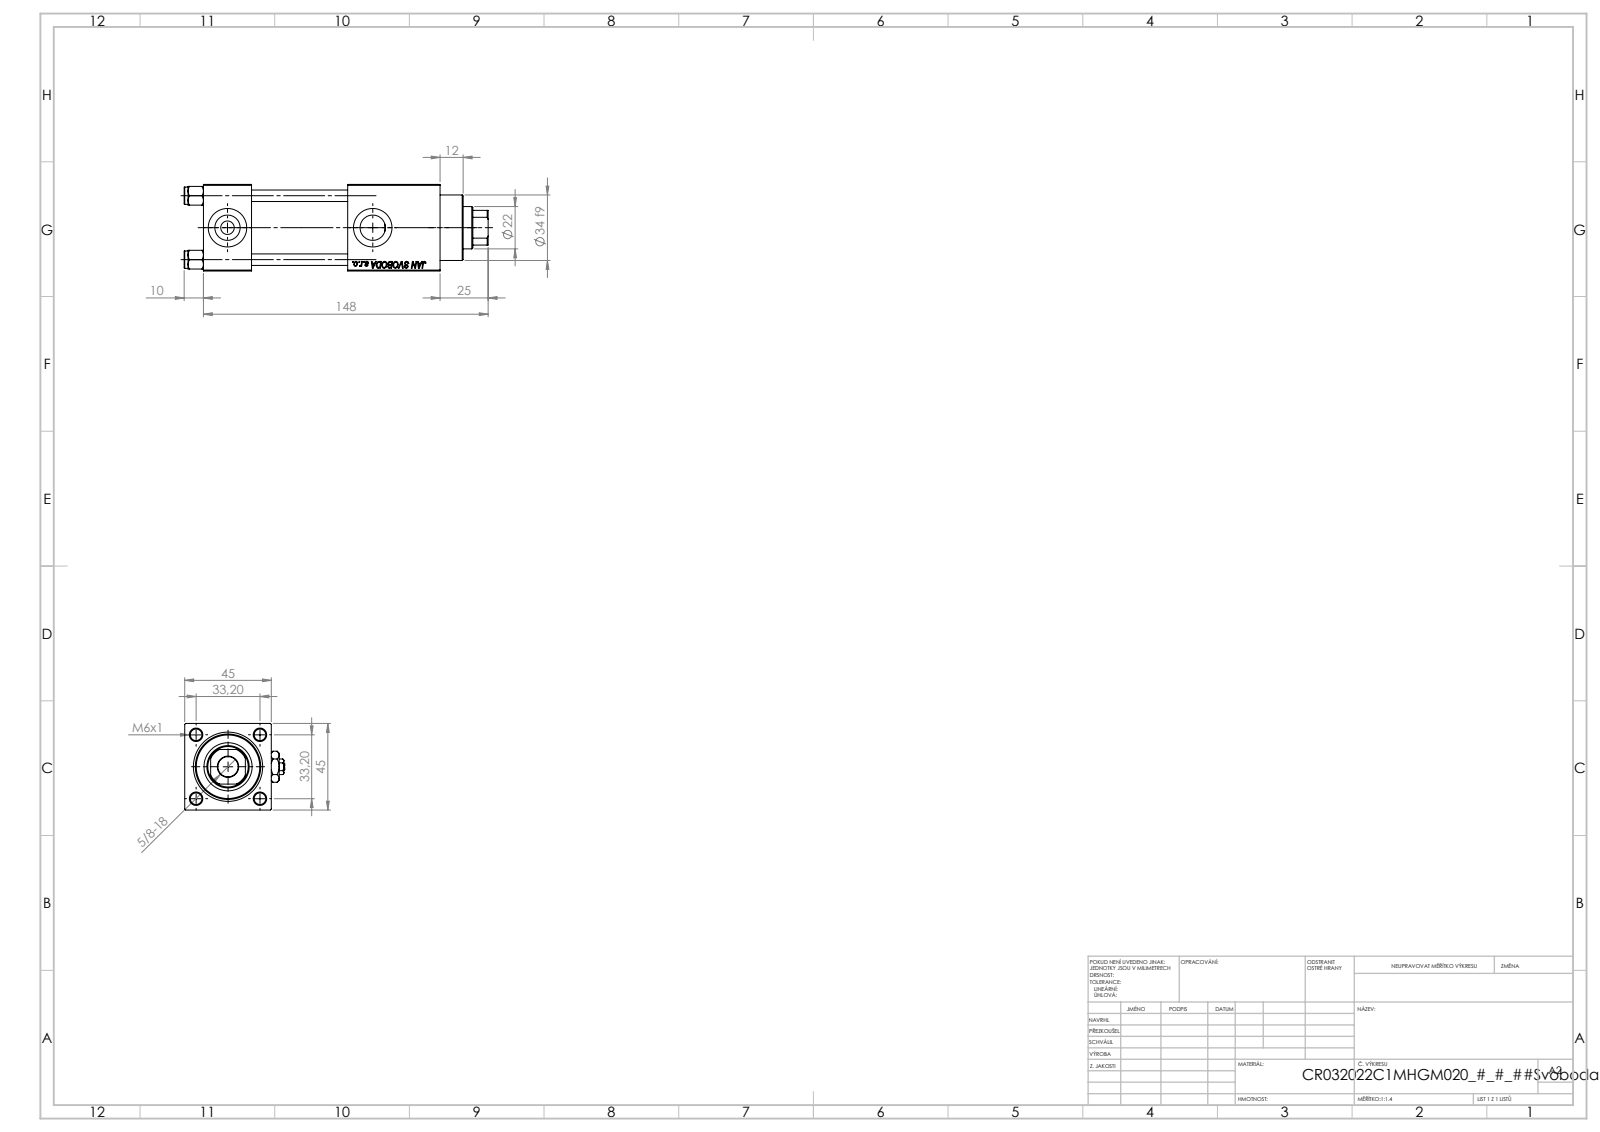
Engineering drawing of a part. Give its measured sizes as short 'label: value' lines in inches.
name: V215CR_VCP_C; V215_VC_A; V215CR_C_Body; NUT_M5_C (+2 more)
written by: SolidWorks 2019 (CONFIG_CONTROL_DESIGN)
unit: in
bodies: 12 solids, 1195 faces (549 planar, 90 cylindrical, 556 other)
size: 6.22 × 2.047 × 1.772
volume: 12.76 in³; area: 111.7 in²
holes: 4× ⌀0.236, 2× ⌀0.276, 2× ⌀0.518, 2× ⌀0.787, 1× ⌀0.413, 1× ⌀0.866, 1× ⌀0.945, 1× ⌀0.984, 1× ⌀1.26, 1× ⌀1.299
bosses: 4× ⌀0.354, 1× ⌀1.496, 1× ⌀1.339
rounds: 1× R0.413
face distances: 1.772, 0.984, 1.969, 4.843, 2.953, 3.858, 1.89, 3.713, 2.728, 0.76
hole spacings: 0.924, 1.307, 1.848, 2.972
